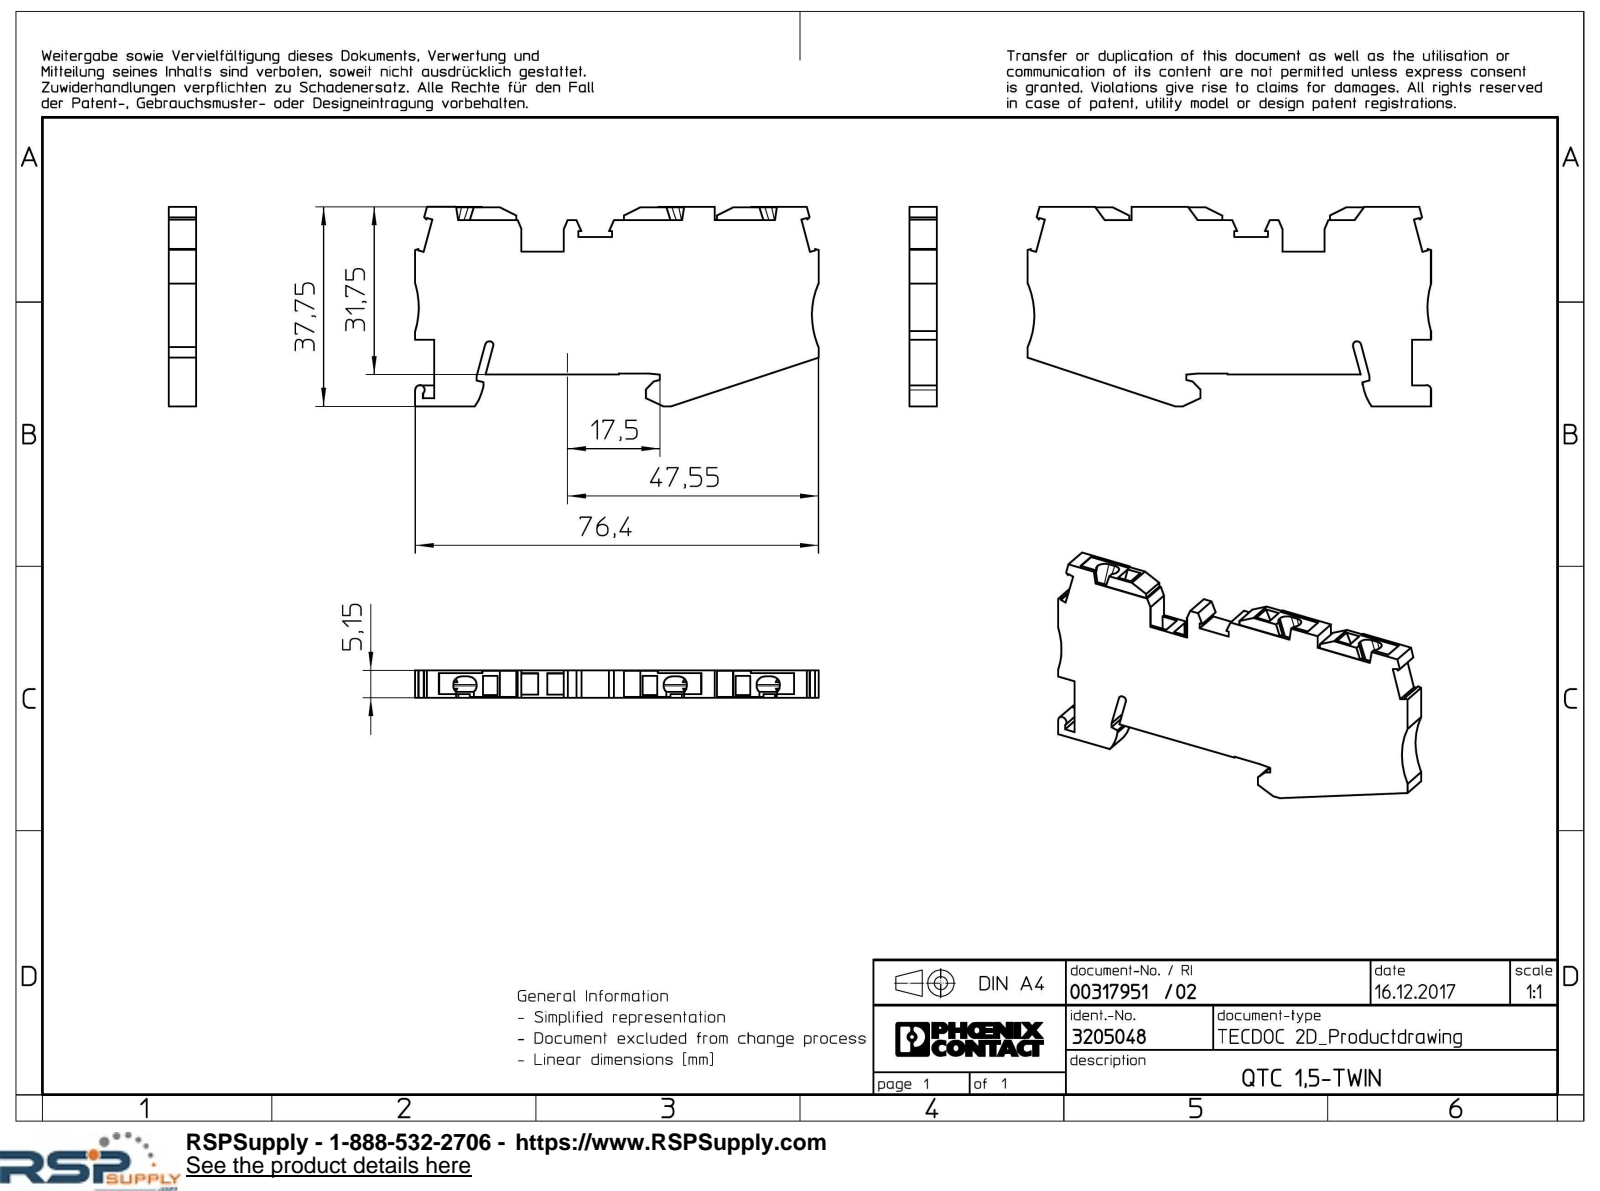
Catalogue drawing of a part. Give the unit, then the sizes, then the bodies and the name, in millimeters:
Units: millimetres
Overall size (bounding box): 76.4 × 37.75 × 5.15
Partial cylindrical surfaces — rounded edges, fillets, slot ends (radius × count): R1.5 ×12, R15 ×2, R0.7 ×1, R0.8 ×1, R0.9 ×1, R9.5 ×1
Main face-to-face distances: 5.15, 4, 3.6, 0.47, 0.57, 3.15, 4.85, 0.5, 1.21, 2.39
Volume: 11 063 mm³ · Surface area: 7 299 mm²
Bodies: 1 solid, 170 faces (152 planar, 18 cylindrical, 0 other)
Part name (STEP PRODUCT): QTC_1.5-TWIN-select
STEP written by: Creo Elements/Direct Modeling 20.1A 29-Sep-2018 (C) Parametric Technology GmbH (AUTOMOTIVE_DESIGN)
